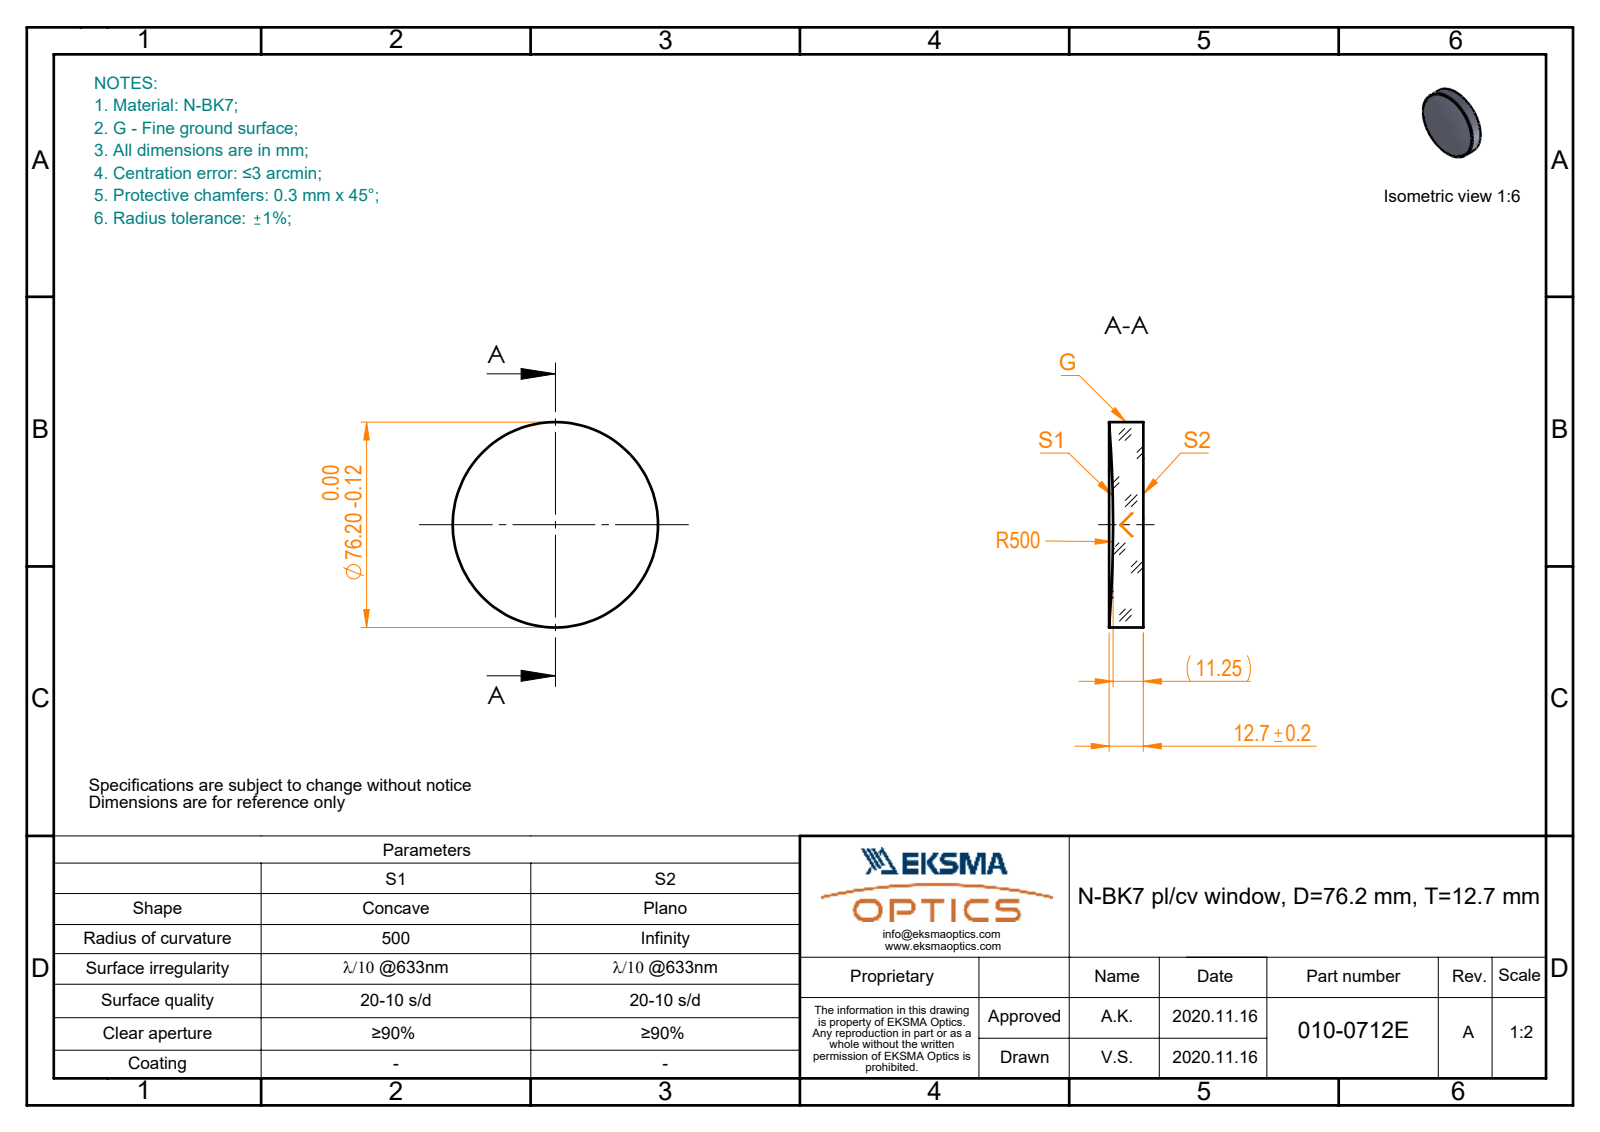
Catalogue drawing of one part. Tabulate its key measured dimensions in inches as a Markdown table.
| quantity | value |
| --- | --- |
| part name | 010-0712E_N-BK7_PCV_window |
| STEP written by | SolidWorks 2019 (CONFIG_CONTROL_DESIGN) |
| units | inches |
| bodies | 1 solid, 5 faces (1 planar, 2 cylindrical, 2 other) |
| overall size | 3 × 3 × 0.5 |
| volume | 3.332 in³ |
| surface area | 18.86 in² |
| round bosses / shafts (diameter × count) | 3 × 1 |
